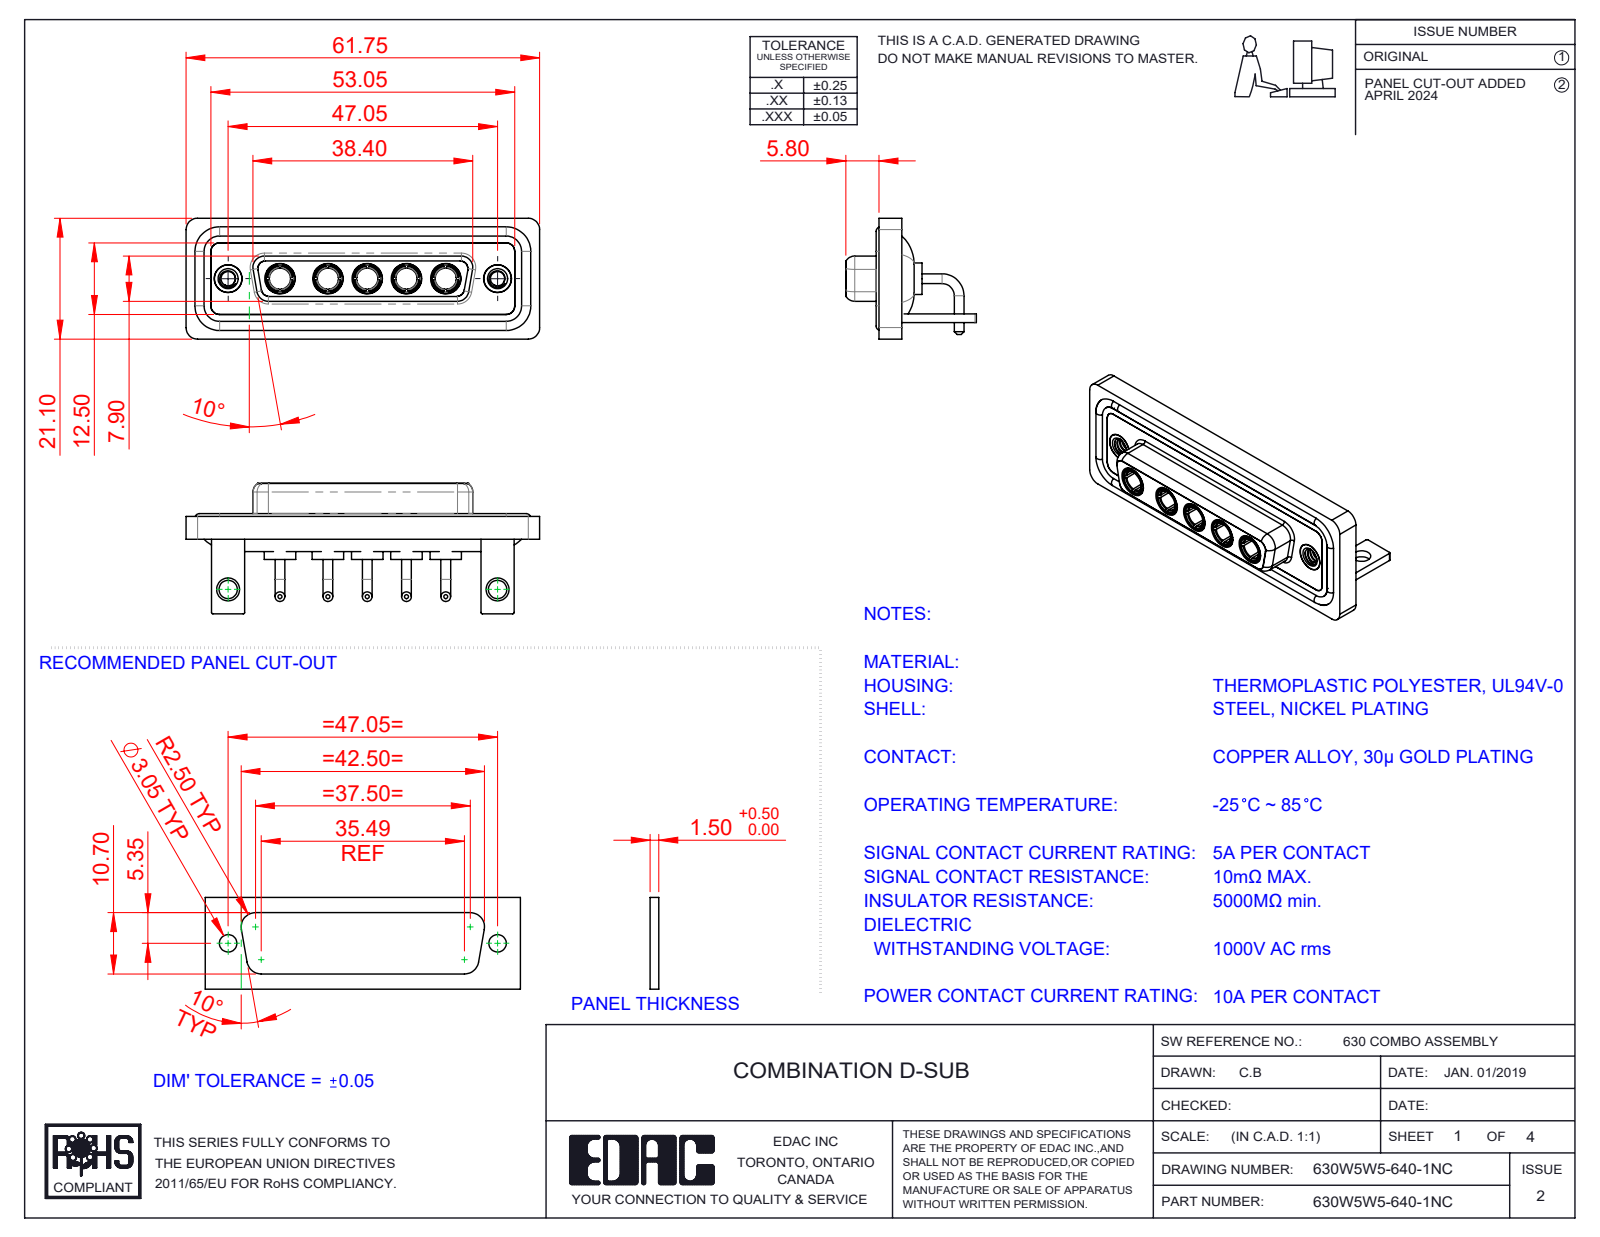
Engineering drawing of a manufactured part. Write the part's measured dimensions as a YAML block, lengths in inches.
part_name: "630Combo Stabilizer Bracket_50 Contacts; 630Combo Waterproof Housing_25 Contacts; 630Combo Threaded Rivet_A; 630W5W5-640-1NC (+4 more)"
step_written_by: "SolidWorks 2023 (CONFIG_CONTROL_DESIGN)"
units: inches
bodies: {solids: 19, faces: 818, planar: 270, cylindrical: 335, other: 213}
overall_size: [2.431, 0.898, 0.831]
volume: 0.519
surface_area: 22.16
round_holes:
  - {diameter: 0.191, count: 7}
  - {diameter: 0.146, count: 5}
  - {diameter: 0.209, count: 5}
  - {diameter: 0.098, count: 2}
  - {diameter: 0.126, count: 2}
  - {diameter: 0.157, count: 2}
  - {diameter: 0.159, count: 2}
  - {diameter: 0.197, count: 2}
round_bosses_or_shafts:
  - {diameter: 0.067, count: 10}
  - {diameter: 0.217, count: 5}
  - {diameter: 0.205, count: 5}
  - {diameter: 0.195, count: 5}
  - {diameter: 0.187, count: 5}
  - {diameter: 0.148, count: 5}
  - {diameter: 0.063, count: 4}
  - {diameter: 0.195, count: 2}
partial_cylinders:
  - {radius: 0.079, count: 19}
  - {radius: 0.059, count: 18}
  - {radius: 0.01, count: 16}
  - {radius: 0.053, count: 8}
  - {radius: 0.063, count: 8}
  - {radius: 0.02, count: 5}
  - {radius: 0.083, count: 5}
  - {radius: 0.024, count: 4}
face_to_face_distances: [0.016, 0.071, 0.059, 0.114, 0.146, 0.161, 0.043, 0.055, 0.063, 0.098]
hole_center_spacings: [0.27, 0.356, 1.496, 1.852, 0.27, 0.33, 0.54, 0.541]
